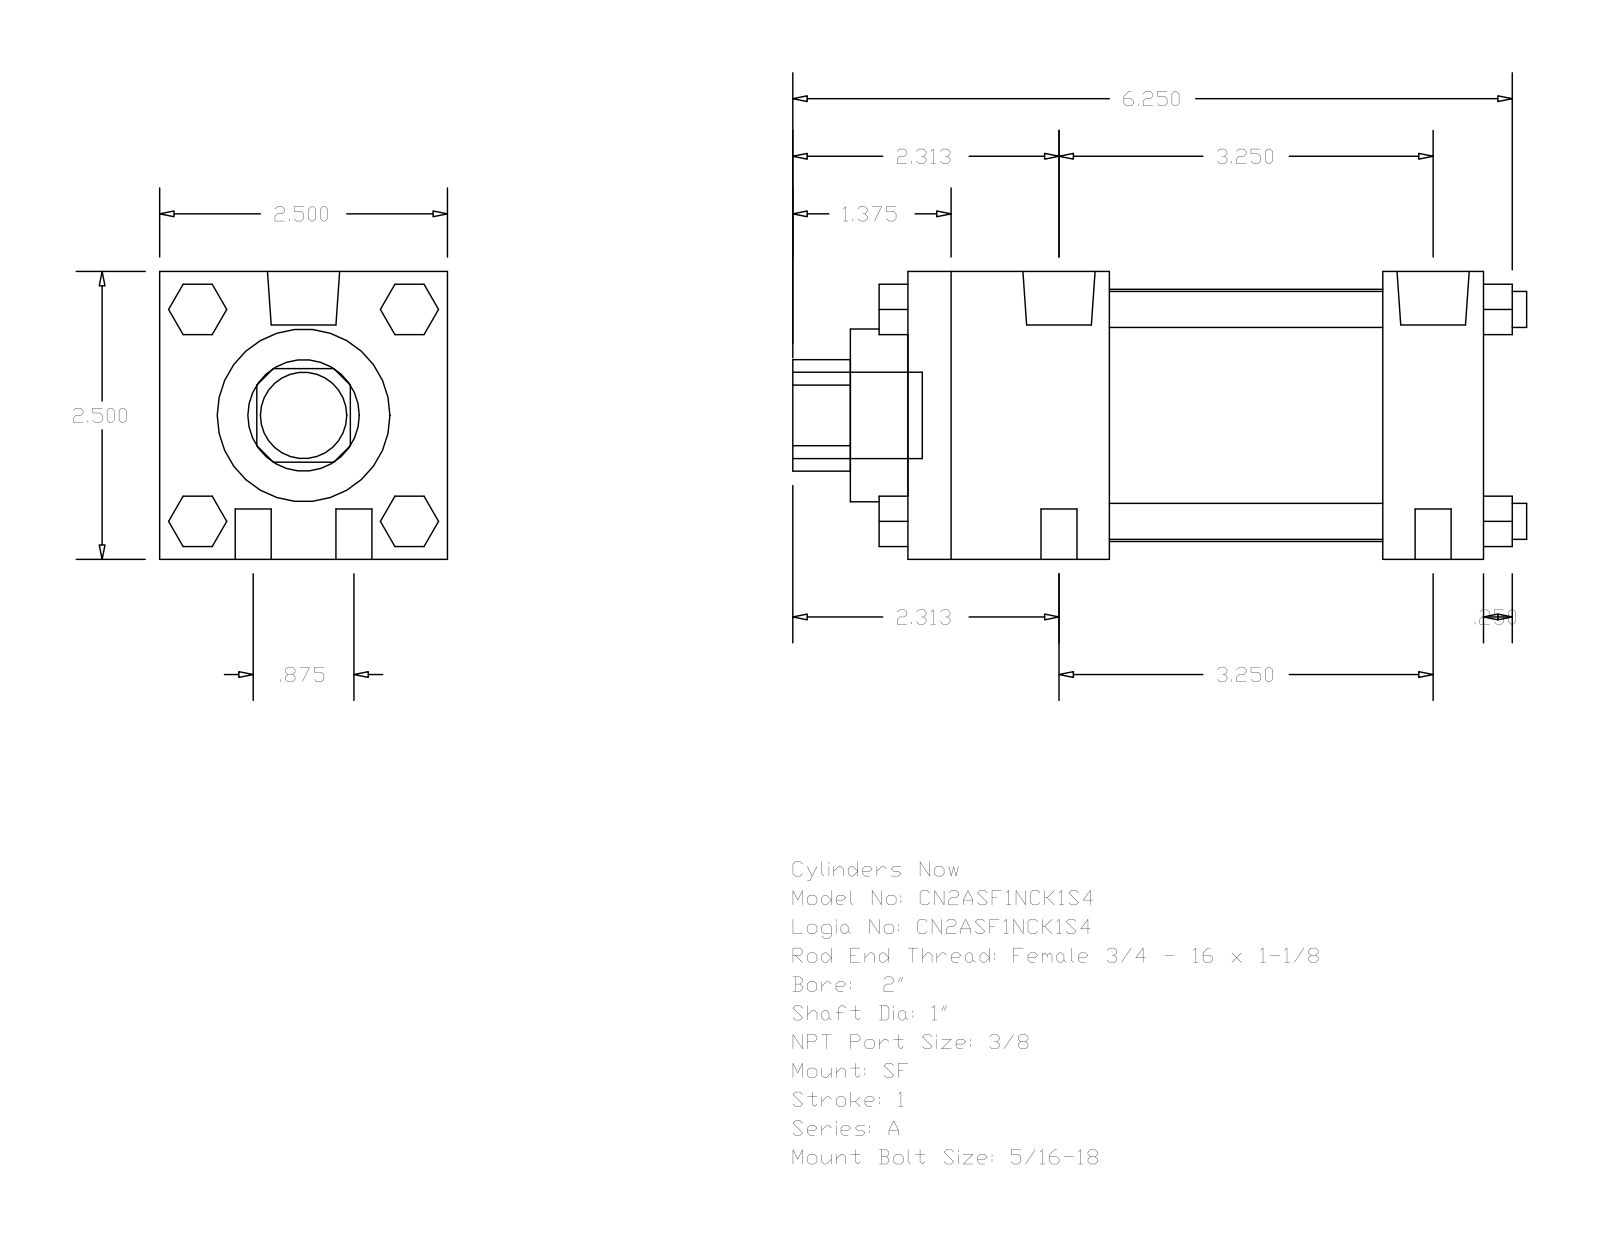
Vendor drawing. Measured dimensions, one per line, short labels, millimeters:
name: A_SF__0200_1
written by: GSSL Pune (CONFIG_CONTROL_DESIGN)
unit: mm
bodies: 0 solids, 124 faces (94 planar, 30 cylindrical, 0 other)
size: 161.93 × 63.5 × 63.5
holes: 1× ⌀25.4, 1× ⌀38.1, 1× ⌀55.63
bosses: 8× ⌀7.94, 2× ⌀15.93, 2× ⌀5.56, 1× ⌀19.05
rounds: 1× R12.29
face distances: 63.5, 127, 104.78, 22.22, 44.45, 60.33, 82.55, 12.7, 139.7, 6.35
